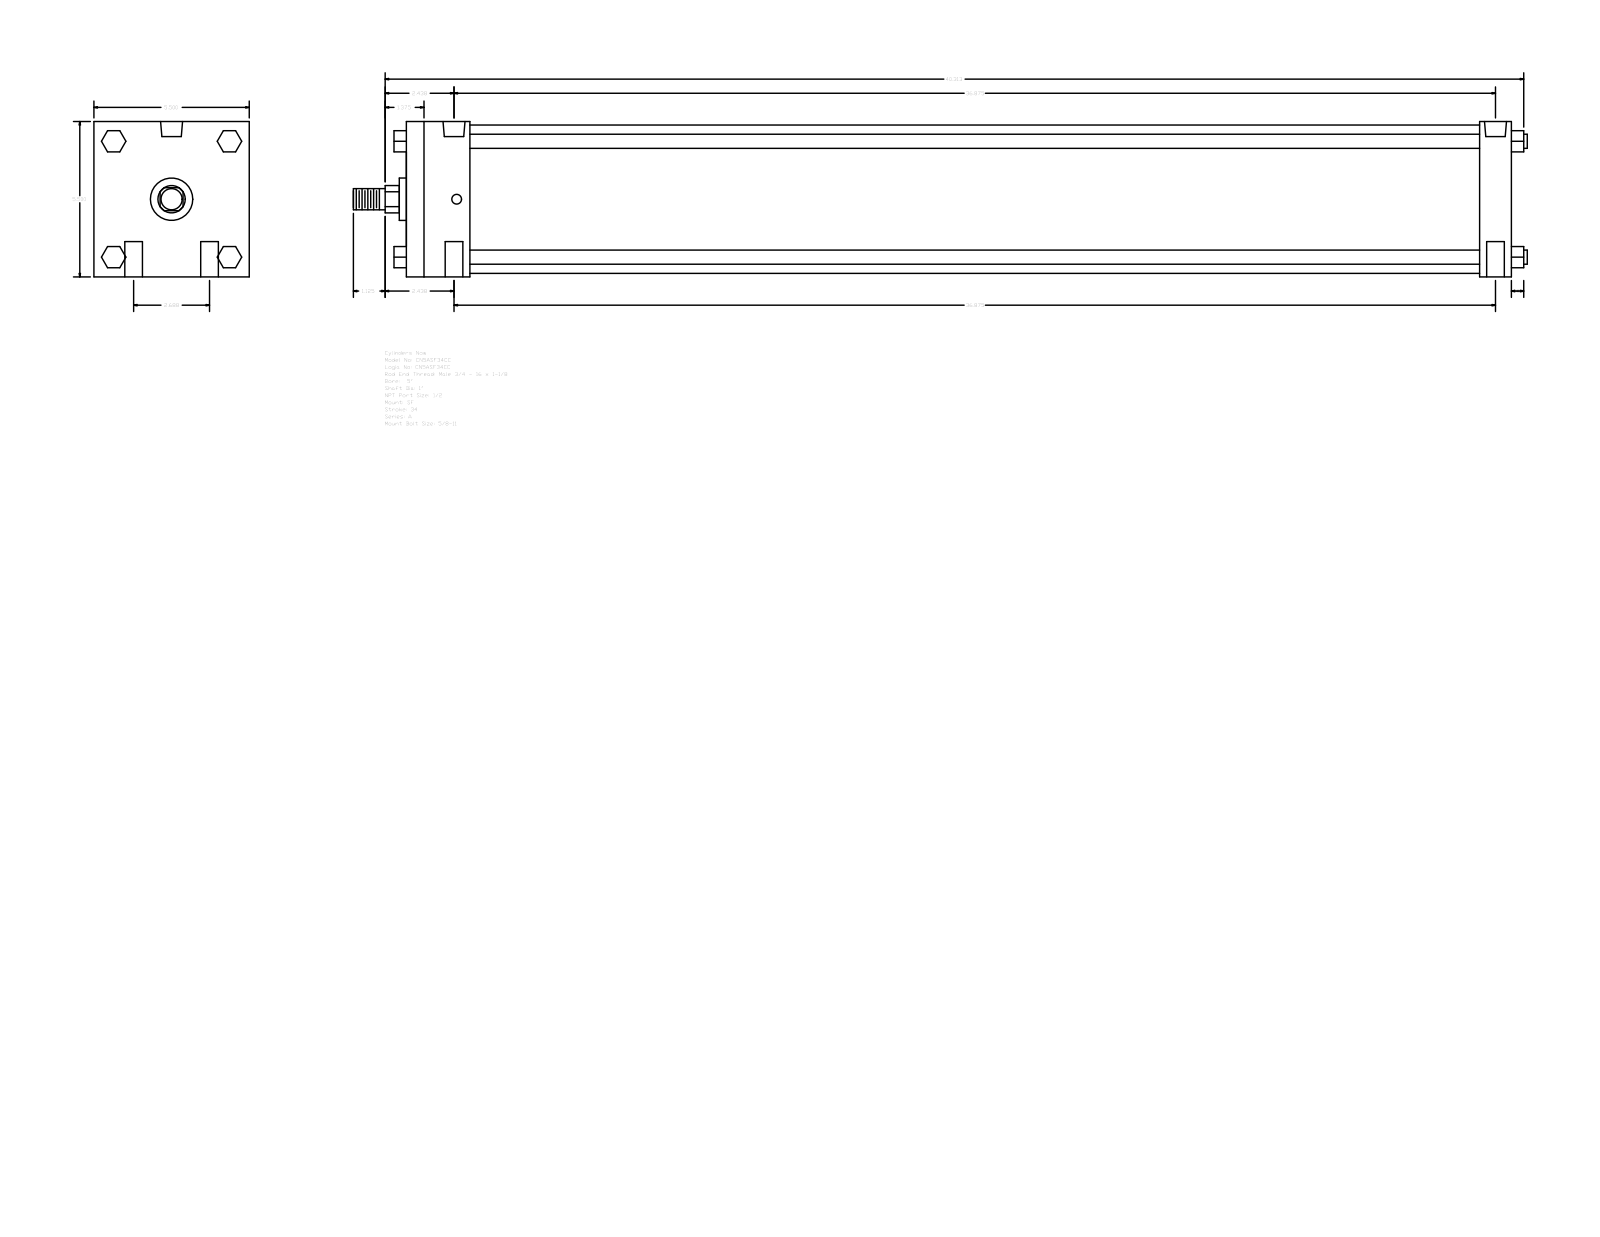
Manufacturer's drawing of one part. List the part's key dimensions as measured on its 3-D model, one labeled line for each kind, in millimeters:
Part name (STEP PRODUCT): A_SF__0500_1
STEP written by: GSSL Pune (CONFIG_CONTROL_DESIGN)
Units: millimetres
Bodies: 0 solids, 124 faces (94 planar, 30 cylindrical, 0 other)
Overall size (bounding box): 1055.69 × 139.7 × 139.7
Round holes (diameter × count): ⌀15.88 ×4, ⌀8.73 ×2, ⌀19.77 ×2
Round bosses / shafts (diameter × count): ⌀12.7 ×4, ⌀133.35 ×1, ⌀38.1 ×1, ⌀25.4 ×1, ⌀19.05 ×1
Partial cylindrical surfaces — rounded edges, fillets, slot ends (radius × count): R12.29 ×1
Main face-to-face distances: 139.7, 993.78, 57.15, 965.2, 908.05, 936.63, 28.58, 19.05, 52.07, 90.18
Hole centre spacings: 34.13, 937.25, 936.63, 68.26, 939.11, 931.85
